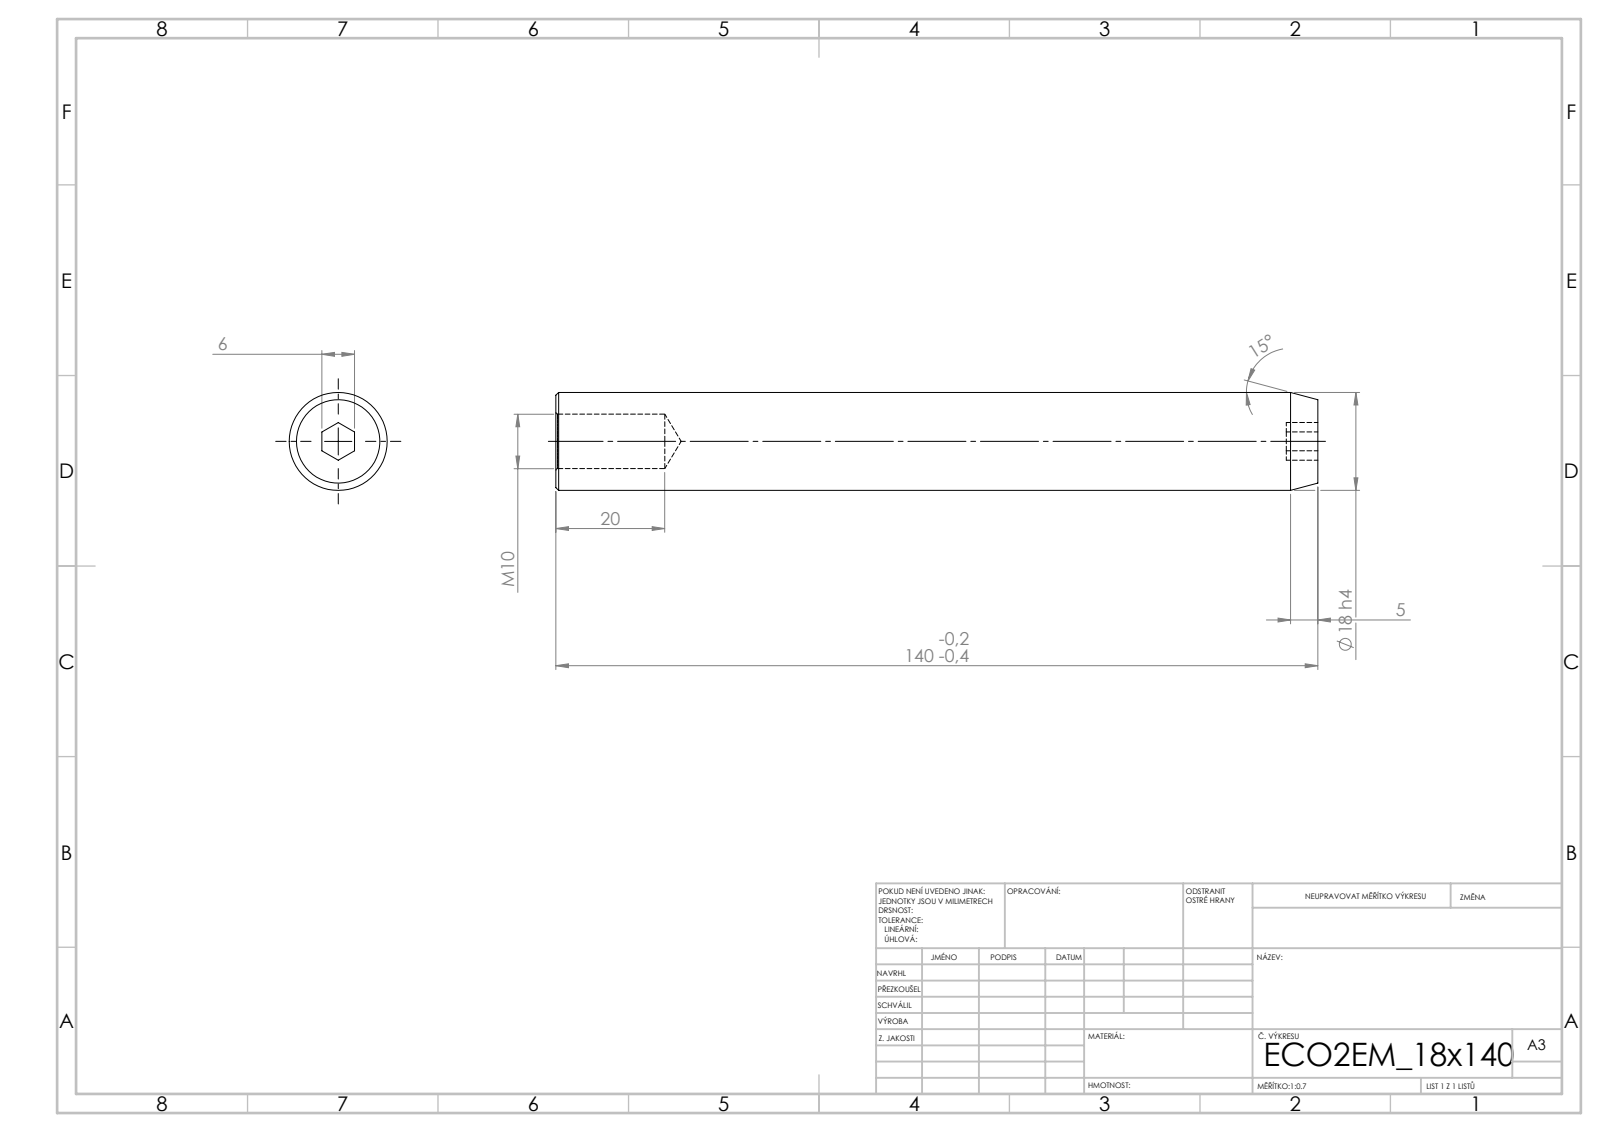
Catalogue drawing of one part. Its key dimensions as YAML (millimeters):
step_written_by: "SolidWorks 2019 (CONFIG_CONTROL_DESIGN)"
units: millimeters
bodies: {solids: 1, faces: 21, planar: 9, cylindrical: 4, other: 8}
overall_size: [140, 18, 18]
volume: 33608
surface_area: 9085
round_holes:
  - {diameter: 10, count: 1}
round_bosses_or_shafts:
  - {diameter: 18, count: 1}
face_to_face_distances: [140, 6, 5.8, 134.2]
